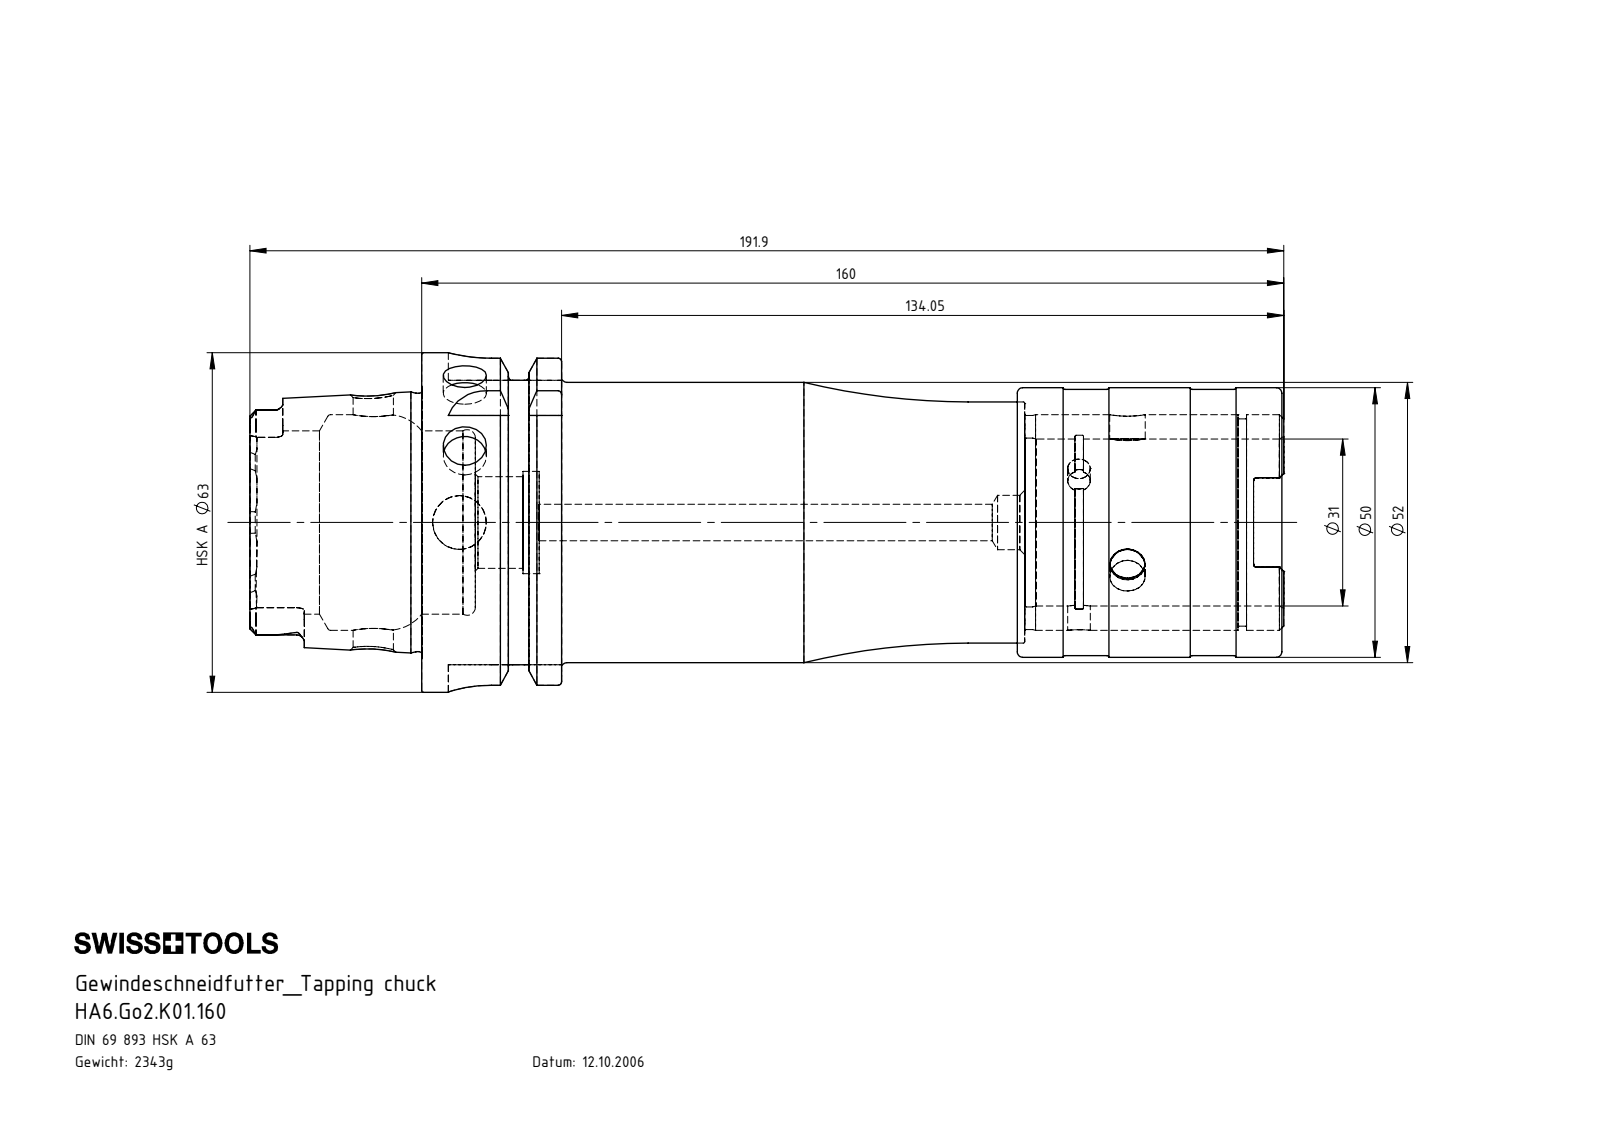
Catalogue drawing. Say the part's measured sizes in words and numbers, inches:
The part is named "HA6.Go2.K01.160; Einbausatz Go2_gespannt; Kugel Go2; Hülse Go2 (+6 more)". Its 3-D file was written by "SolidWorks 2011 (AUTOMOTIVE_DESIGN)". It is 10 solids with 391 faces: 90 planar, 121 cylindrical and 180 other. Overall it measures 7.555 by 2.48 by 2.48 inches. Its volume is 18.21 cubic inches and its surface area 110.6 square inches. Round holes: 3 of diameter 0.165, 3 of diameter 0.26, 2 of diameter 0.315, 1 of diameter 0.098, 1 of diameter 0.268, 1 of diameter 0.295, 1 of diameter 0.394, 1 of diameter 0.398, 1 of diameter 0.669, 1 of diameter 0.748, 1 of diameter 1.22, 1 of diameter 1.232. Round bosses or shafts: 1 of diameter 2.48, 1 of diameter 2.163, 1 of diameter 2.047, 1 of diameter 1.969, 1 of diameter 1.945, 1 of diameter 1.887, 1 of diameter 1.762, 1 of diameter 1.575. Partial cylindrical surfaces (rounded edges, fillets, slot ends): 6 of radius 0.055, 4 of radius 0.113, 4 of radius 0.315, 3 of radius 0.122, 2 of radius 0.02. The main face-to-face distances are 0.63, 4.907, 3.961, 4.409, 0.498, 1.022, 3.388, 3.886, 4.435, 3.413. The hole center spacings are 0.354, 5.157, 5.512.
